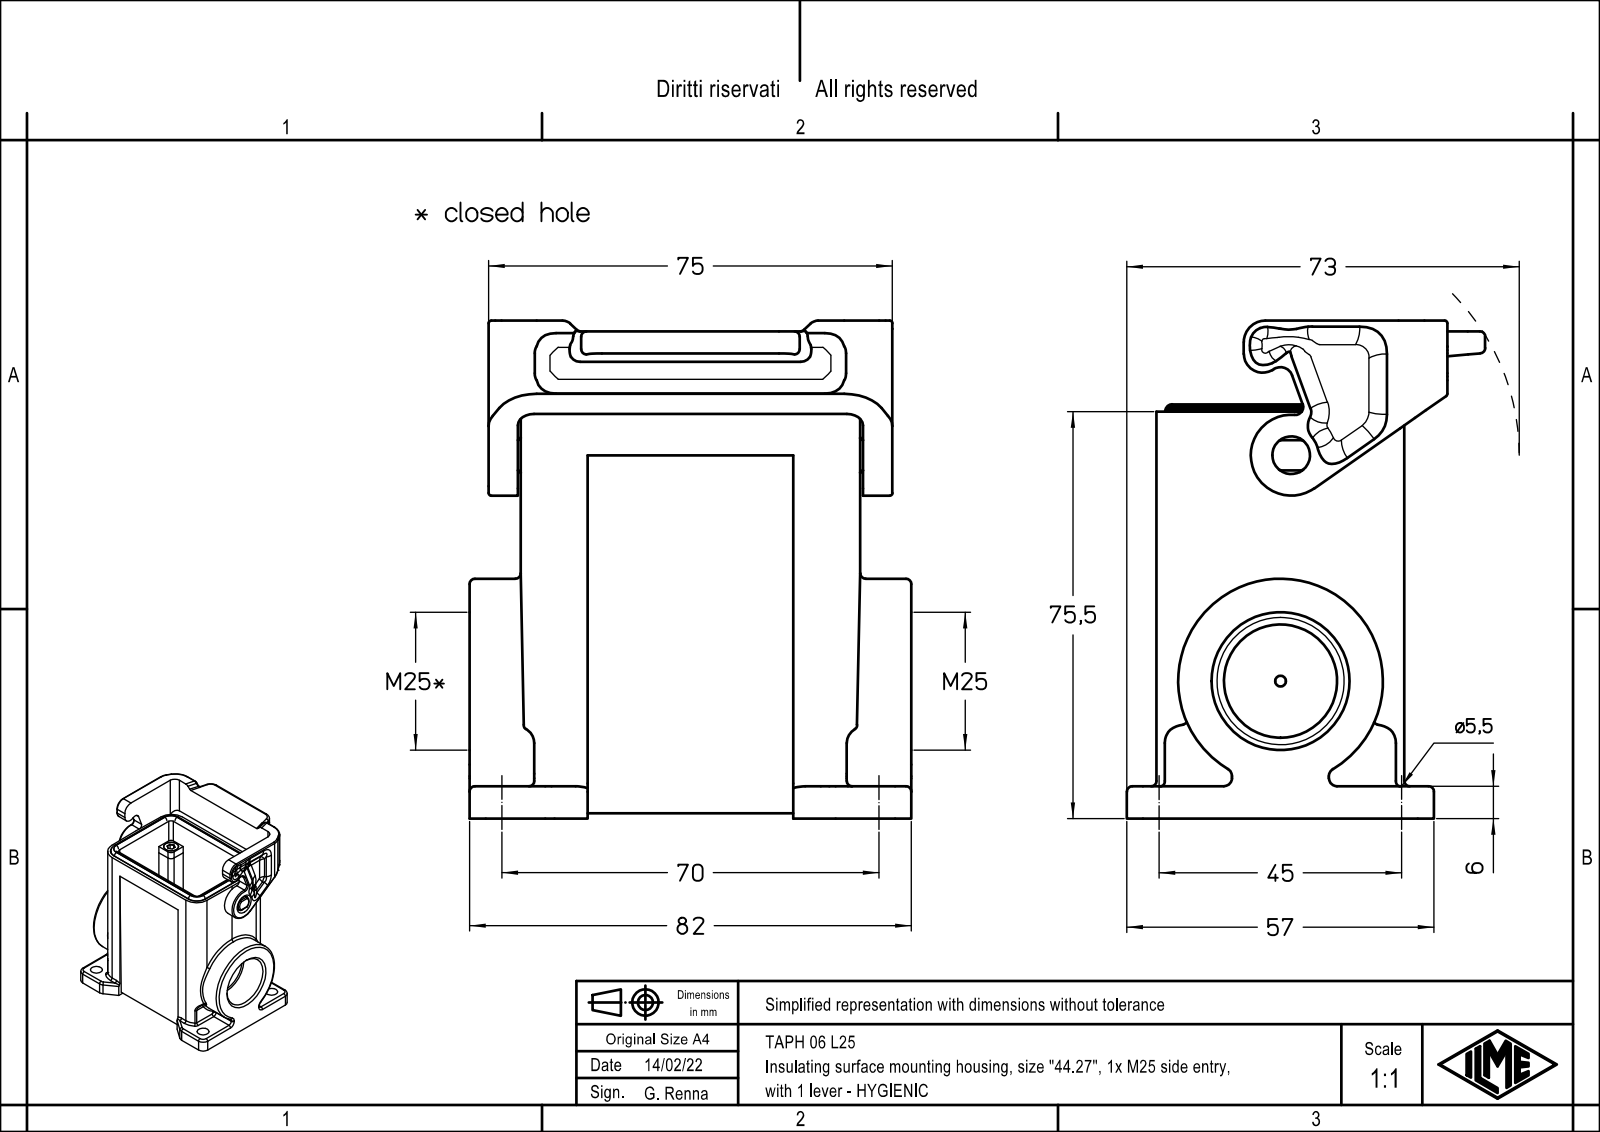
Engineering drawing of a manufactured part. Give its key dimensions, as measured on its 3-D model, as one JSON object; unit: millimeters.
{"part_name": "TAPH 06 L25", "step_written_by": "Creo Elements/Direct Modeling 20.1B 02-Apr-2019 (C) Parametric Technology GmbH (AUTOMOTIVE_DESIGN)", "units": "millimeters", "bodies": {"solids": 1, "faces": 326, "planar": 162, "cylindrical": 128, "other": 36}, "overall_size": [92.4, 82, 66.5], "volume_mm3": 138276, "surface_area_mm2": 47533, "round_holes": [[5.5, 4], [21, 1], [23.6, 1]], "round_bosses_or_shafts": [[38, 1]], "partial_cylinders_radius": [[3, 17], [2, 10], [1.5, 9], [1, 8], [1.3, 8], [0.5, 4], [6, 4], [7, 4]], "face_to_face_distances": [46, 5.4, 40.6, 40.59, 35.19, 5.41, 5.5, 14.9, 1, 9], "hole_center_spacings": [45, 70, 83.22]}
